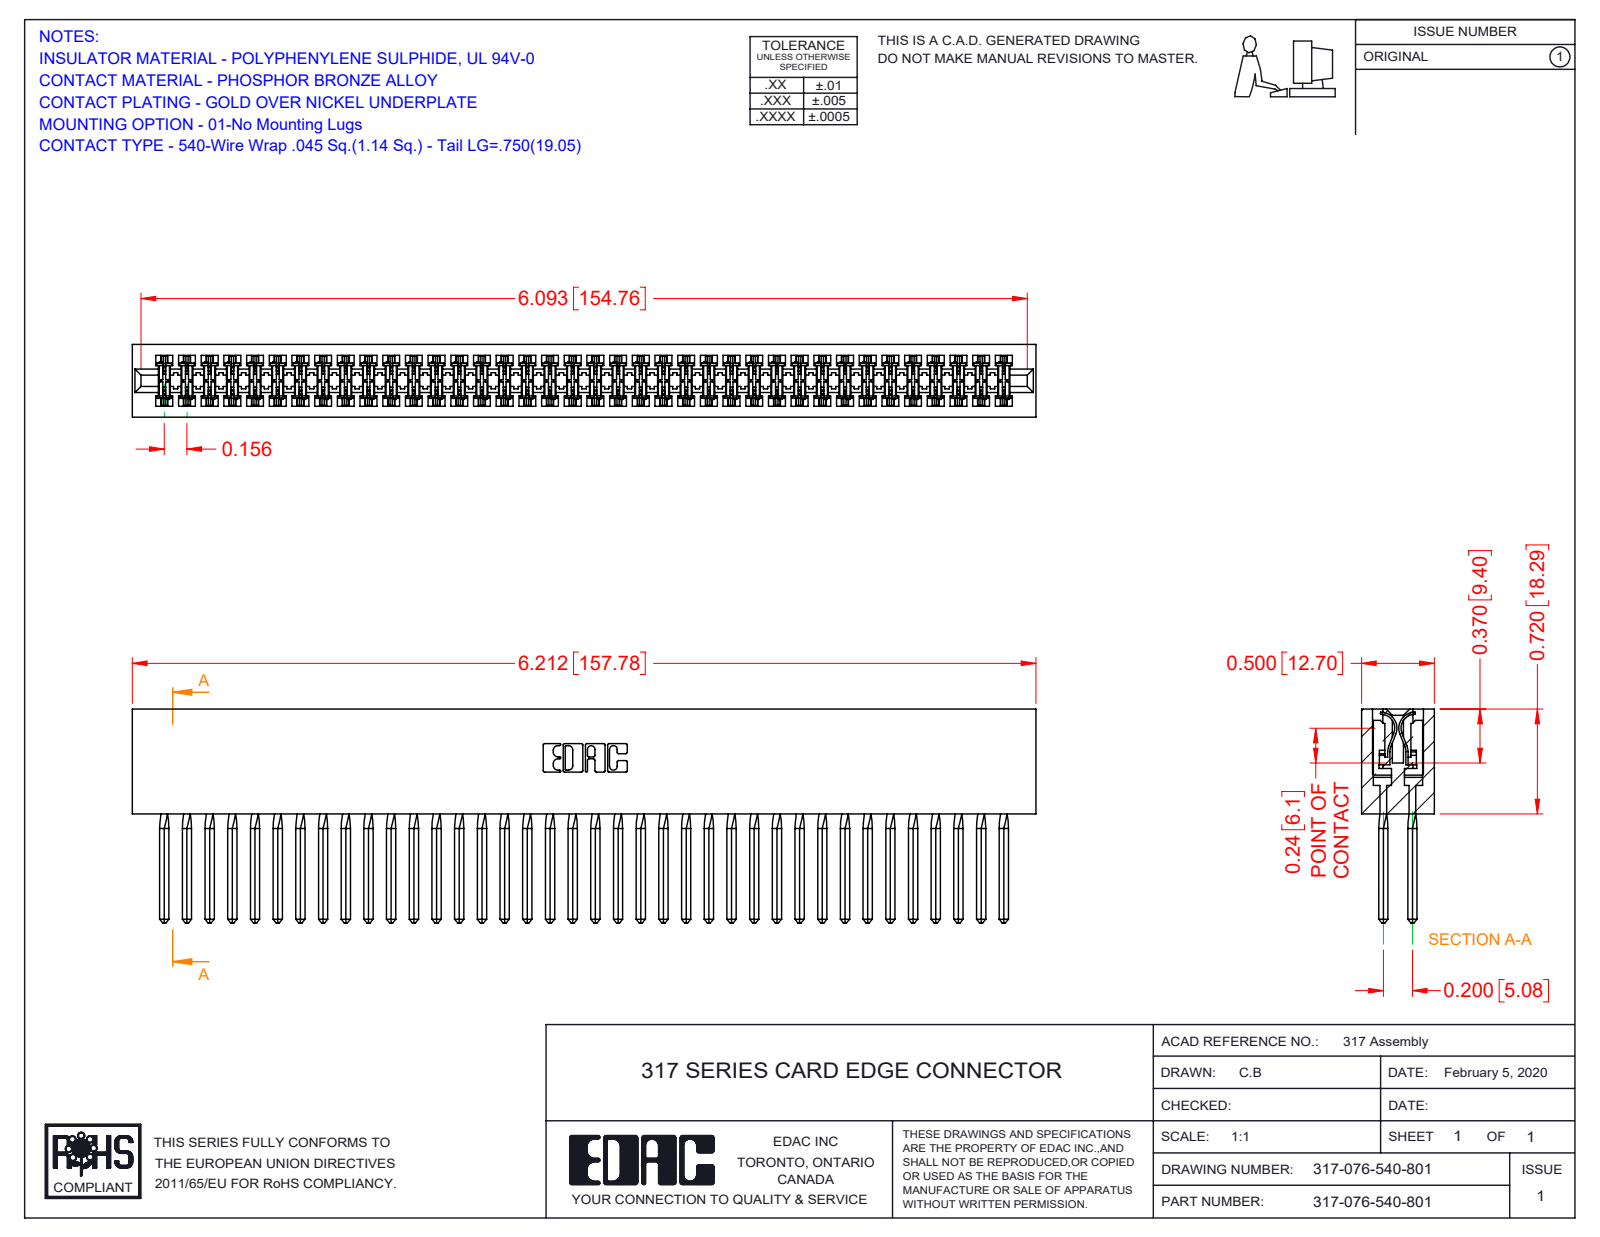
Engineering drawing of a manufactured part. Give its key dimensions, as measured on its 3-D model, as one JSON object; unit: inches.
{"part_name": "317-076-540-801; 317-290-001_540; 317 Part_Lugless", "step_written_by": "SolidWorks 2016 (CONFIG_CONTROL_DESIGN)", "units": "inches", "bodies": {"solids": 77, "faces": 6854, "planar": 5598, "cylindrical": 952, "other": 304}, "overall_size": [6.212, 1.47, 0.5], "volume_in3": 1.717, "surface_area_in2": 65.19, "partial_cylinders_radius": [[0.015, 152], [0.01, 22], [0.007, 6], [0.031, 6], [0.026, 3], [0.095, 2], [0.1, 2], [0.11, 2]], "face_to_face_distances": [0.075, 0.5, 0.425, 0.35, 0.195, 0.094, 0.11, 0.2, 0.115, 0.131]}
